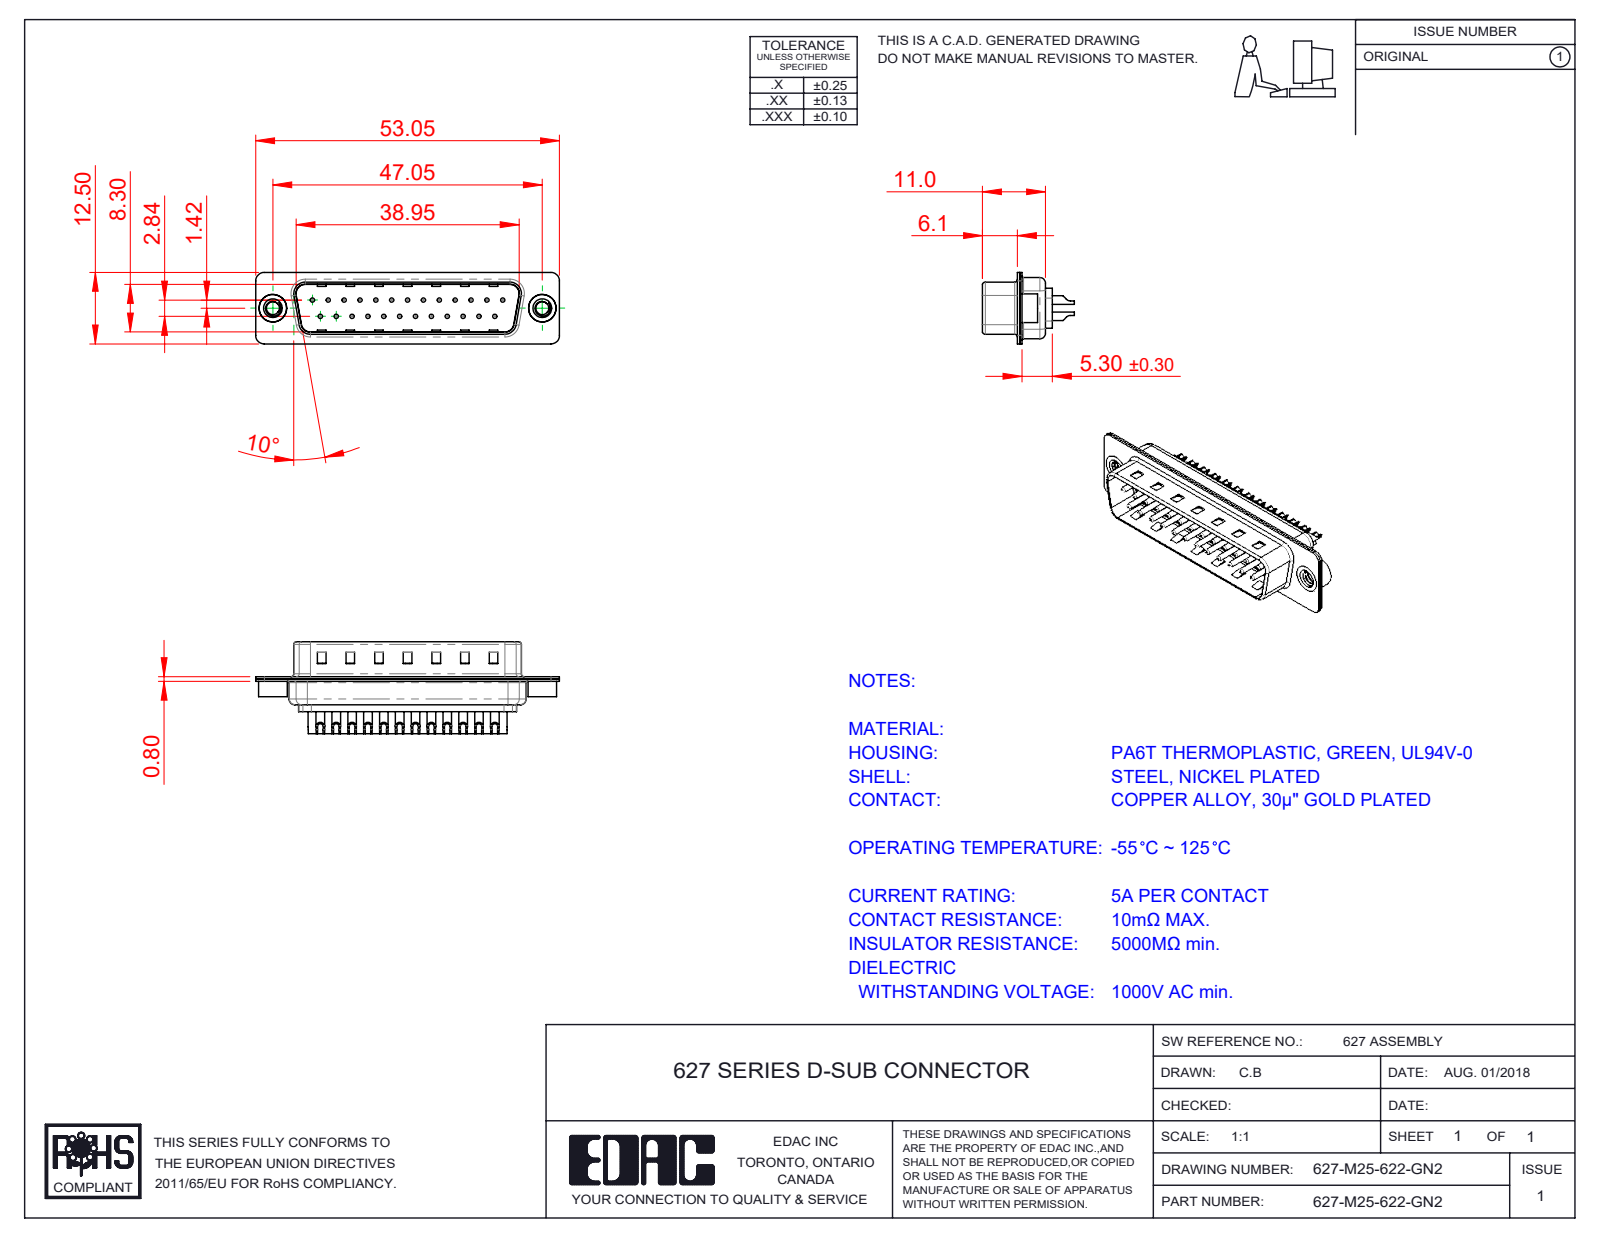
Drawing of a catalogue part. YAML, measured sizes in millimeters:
part_name: "627M Shell Rear_25 Contacts; 627M Contact Row 1_22; 627M Housing_25 Contacts; 627M Shell Front_25 Contacts (+3 more)"
step_written_by: "SolidWorks 2020 (CONFIG_CONTROL_DESIGN)"
units: millimeters
bodies: {solids: 30, faces: 1301, planar: 396, cylindrical: 537, other: 368}
overall_size: [53.05, 16.05, 12.5]
volume: 2776
surface_area: 7078
round_holes:
  - {diameter: 0.75, count: 25}
  - {diameter: 1, count: 25}
  - {diameter: 1.6, count: 25}
  - {diameter: 2, count: 25}
  - {diameter: 2.26, count: 2}
  - {diameter: 4, count: 2}
  - {diameter: 4.8, count: 2}
round_bosses_or_shafts:
  - {diameter: 1.5, count: 25}
  - {diameter: 5, count: 2}
  - {diameter: 4.9, count: 2}
partial_cylinders:
  - {radius: 1.5, count: 16}
  - {radius: 2, count: 12}
  - {radius: 0.5, count: 8}
  - {radius: 1.6, count: 8}
  - {radius: 1, count: 6}
  - {radius: 0.25, count: 4}
  - {radius: 0.6, count: 4}
  - {radius: 0.65, count: 4}
face_to_face_distances: [0.4, 0.8, 9.5, 9.1, 8.7, 9.9, 1.2, 0.75, 0.35, 6.1]
hole_center_spacings: [3.16, 2.77, 5.54, 8.31, 11.08, 13.85, 16.62, 5.03]
